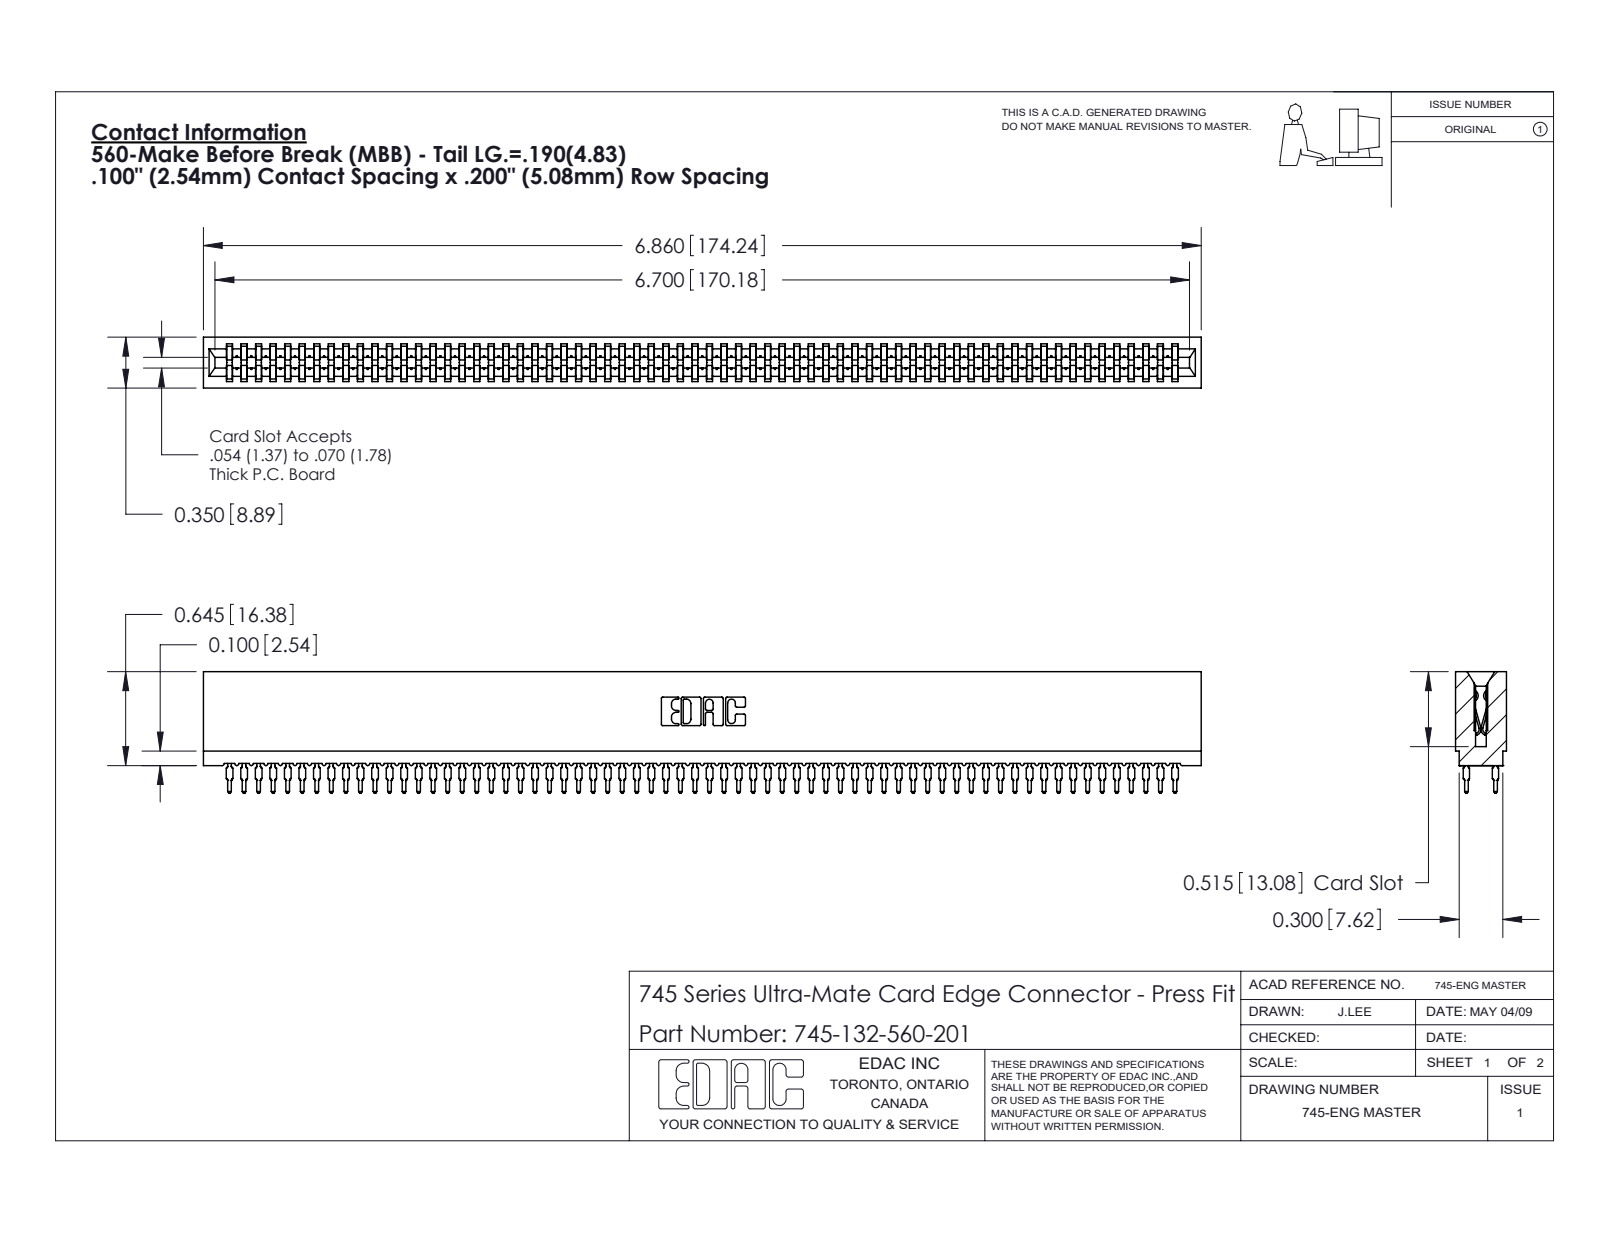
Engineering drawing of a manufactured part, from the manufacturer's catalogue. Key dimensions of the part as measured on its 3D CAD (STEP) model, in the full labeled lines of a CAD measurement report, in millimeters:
Part name (STEP PRODUCT): 745-292-001_560; 745-132-560-201; 745 Part_Insulator Option - 01
STEP written by: SolidWorks 2020 (CONFIG_CONTROL_DESIGN)
Units: millimetres
Bodies: 133 solids, 13097 faces (6787 planar, 2878 cylindrical, 3432 other)
Overall size (bounding box): 174.2 × 21.2 × 8.9
Volume: 16 000 mm³ · Surface area: 35 240 mm²
Partial cylindrical surfaces — rounded edges, fillets, slot ends (radius × count): R0.5 ×264, R0.4 ×132, R0.3 ×22, R0.1 ×8, R0.3 ×8, R0.2 ×6, R0.8 ×6, R0.7 ×3
Main face-to-face distances: 8.9, 1.6, 7.3, 1.1, 7.7, 0.5, 6.2, 3.5, 5.4, 2.4
